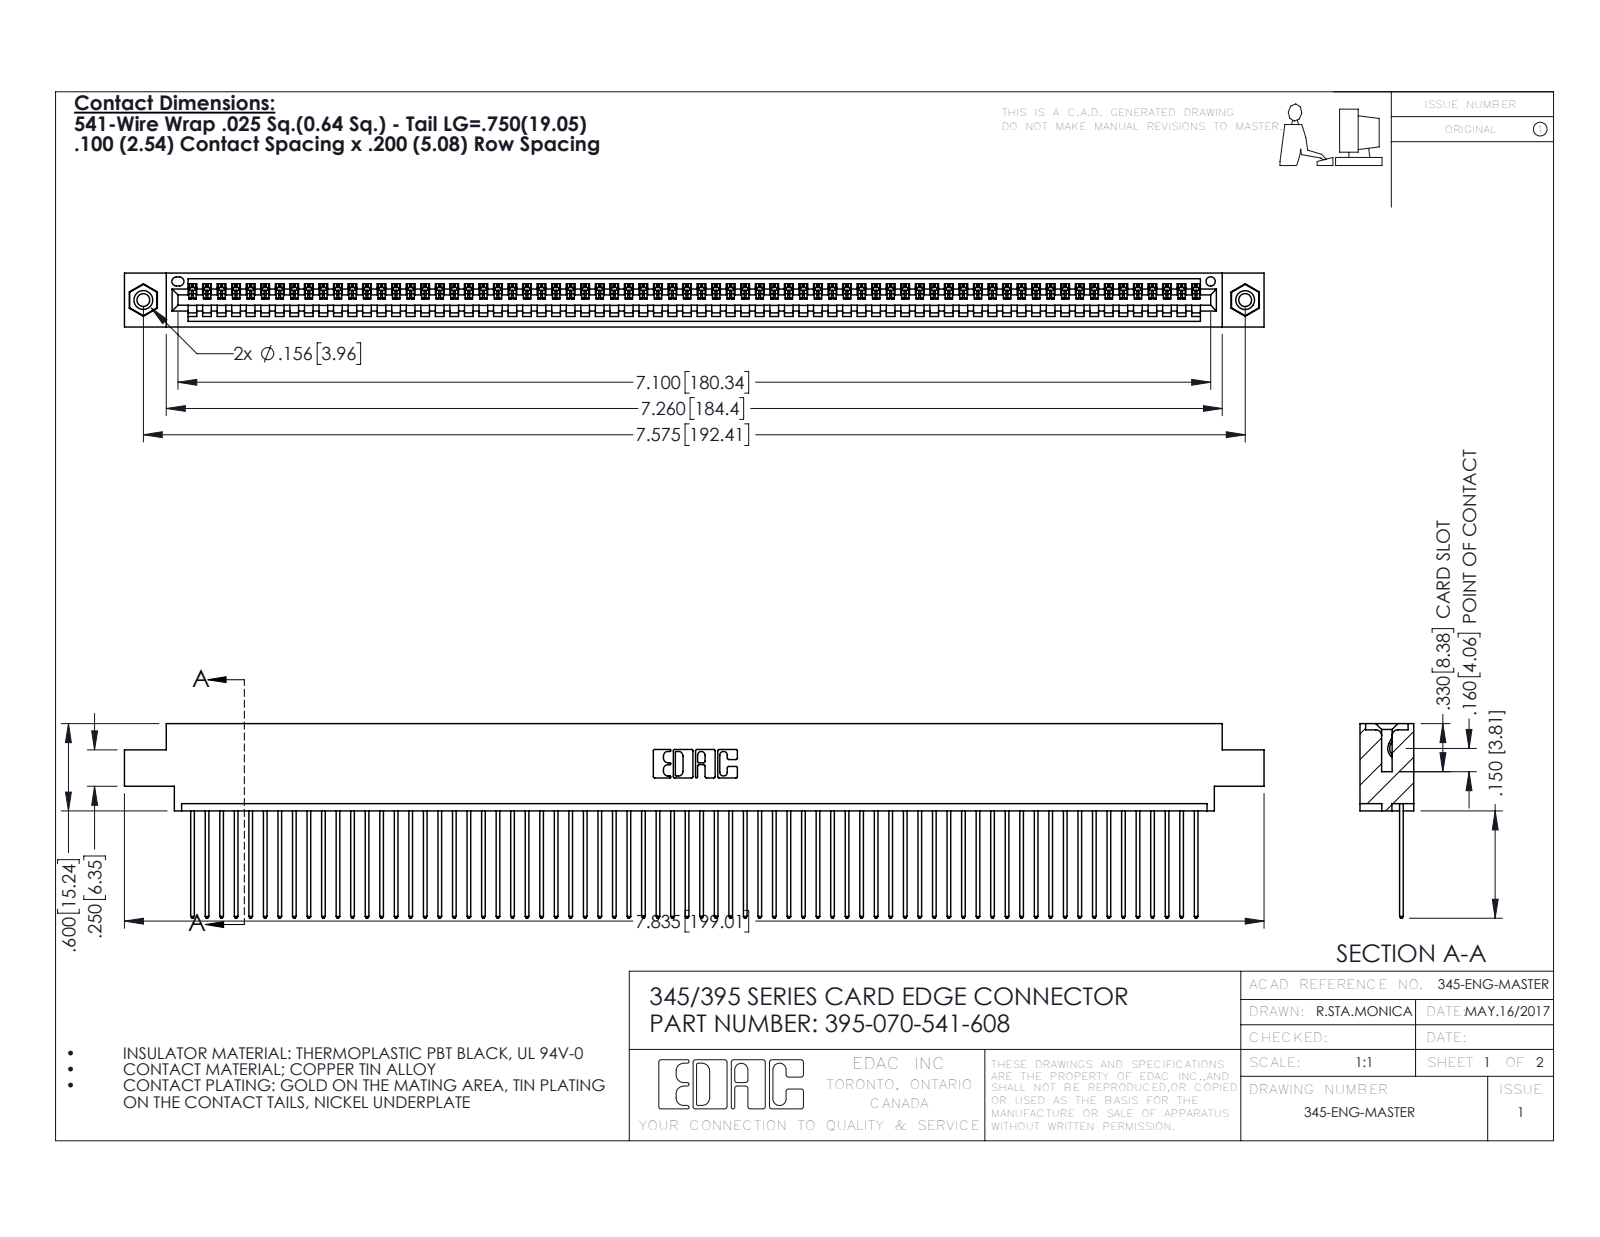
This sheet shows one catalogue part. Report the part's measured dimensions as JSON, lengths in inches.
{"part_name": "345-250-001_345-250-003-102; 345 Part_0.170 Offset - 0.156 Dia-TI; 345-292-001_345-293-141; 395-070-541-608", "step_written_by": "SolidWorks 2016 (CONFIG_CONTROL_DESIGN)", "units": "inches", "bodies": {"solids": 73, "faces": 4250, "planar": 2916, "cylindrical": 1318, "other": 16}, "overall_size": [7.835, 1.337, 0.37], "volume_in3": 1.174, "surface_area_in2": 42.56, "round_holes": [[0.089, 2], [0.125, 2], [0.156, 2], [0.064, 1]], "round_bosses_or_shafts": [[0.155, 2]], "partial_cylinders_radius": [[0.006, 140], [0.01, 140], [0.01, 22], [0.007, 6], [0.031, 6], [0.026, 3], [0.031, 2], [0.04, 2]], "face_to_face_distances": [0.072, 0.298, 0.098, 0.272, 0.025, 0.37, 0.2, 0.225, 0.175, 0.149], "hole_center_spacings": [0.27, 7.339, 7.575]}
